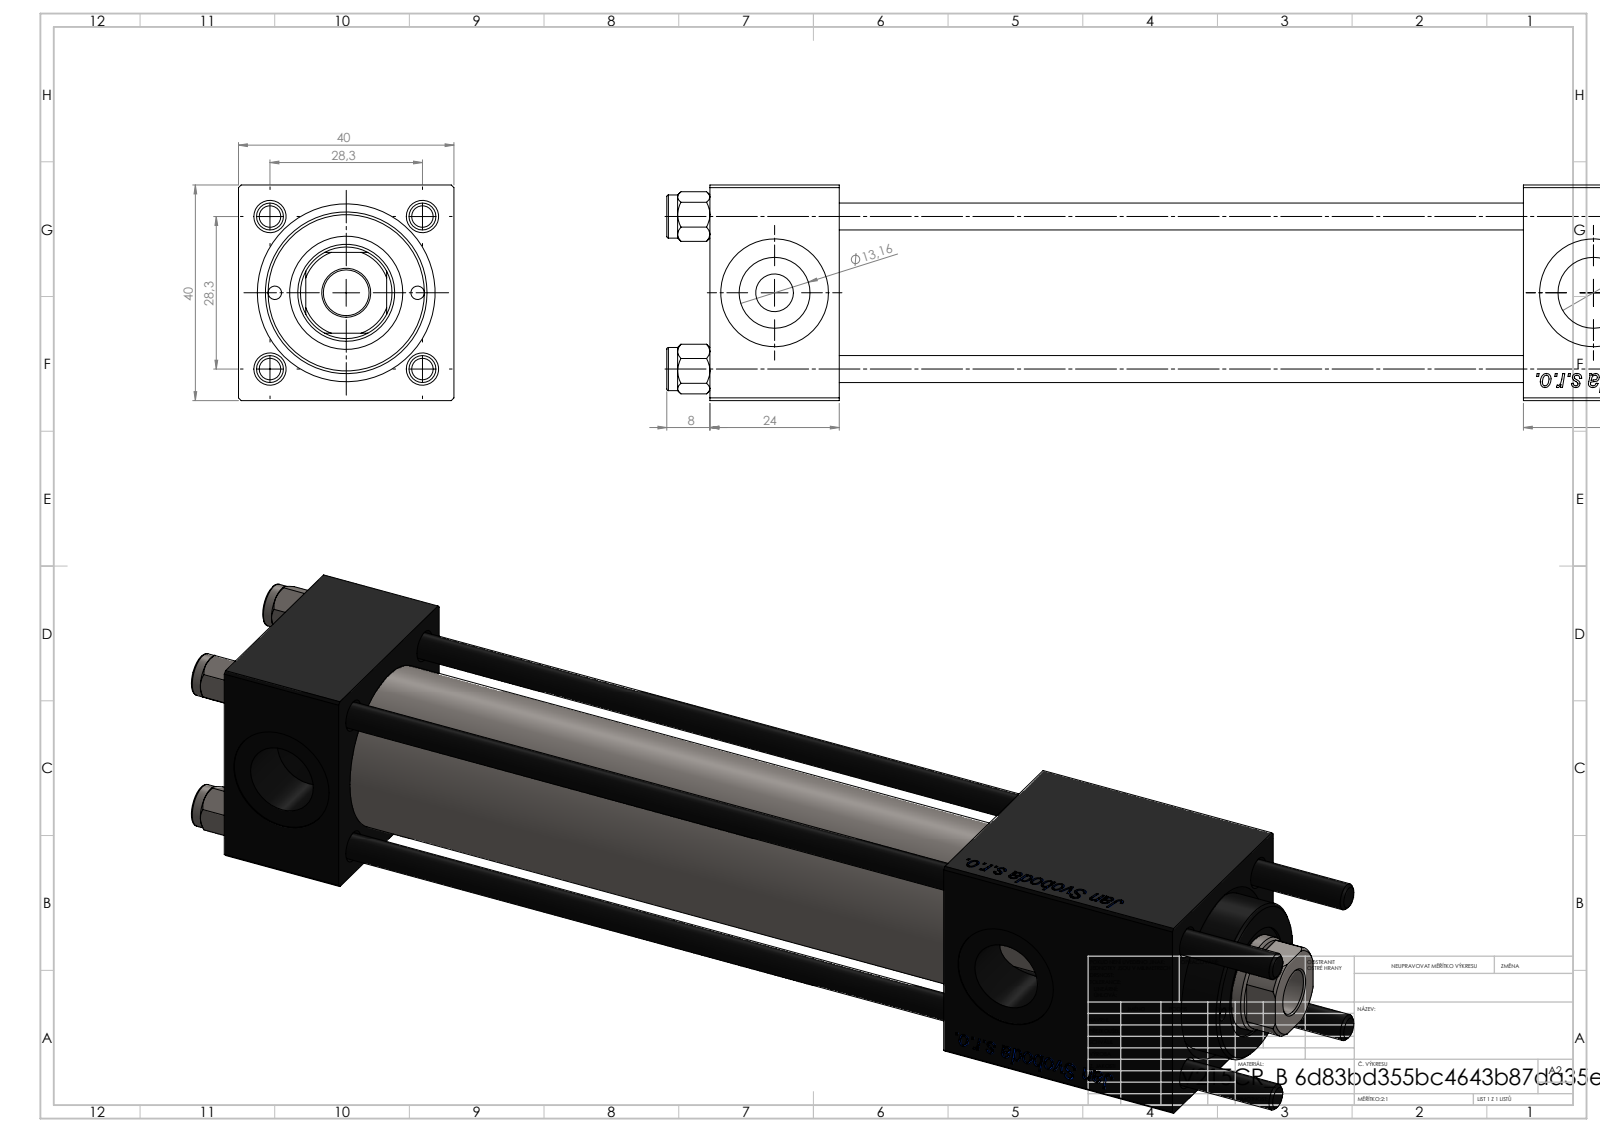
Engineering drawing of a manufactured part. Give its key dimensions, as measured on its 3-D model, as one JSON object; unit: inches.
{"part_name": "V215CR_B-1; V215_VC_A; NUT_M5_B; V215CR_B_TYCINKA (+1 more)", "step_written_by": "SolidWorks 2019 (CONFIG_CONTROL_DESIGN)", "units": "inches", "bodies": {"solids": 11, "faces": 1158, "planar": 430, "cylindrical": 80, "other": 648}, "overall_size": [8.898, 1.575, 1.575], "volume_in3": 12.21, "surface_area_in2": 131.3, "round_holes": [[0.197, 4], [0.787, 3], [0.098, 2], [0.276, 2], [0.518, 2], [0.335, 1], [0.709, 1], [0.827, 1], [0.984, 1], [1.181, 1]], "round_bosses_or_shafts": [[0.315, 4], [1.22, 1]], "partial_cylinders_radius": [[0.335, 1]], "face_to_face_distances": [1.575, 0.945, 5.945, 5, 6.705, 5.76, 0.76, 7.835, 6.89, 1.89], "hole_center_spacings": [0.558, 0.788, 1.114, 1.214, 0.522, 1.576, 1.043, 5.984]}
